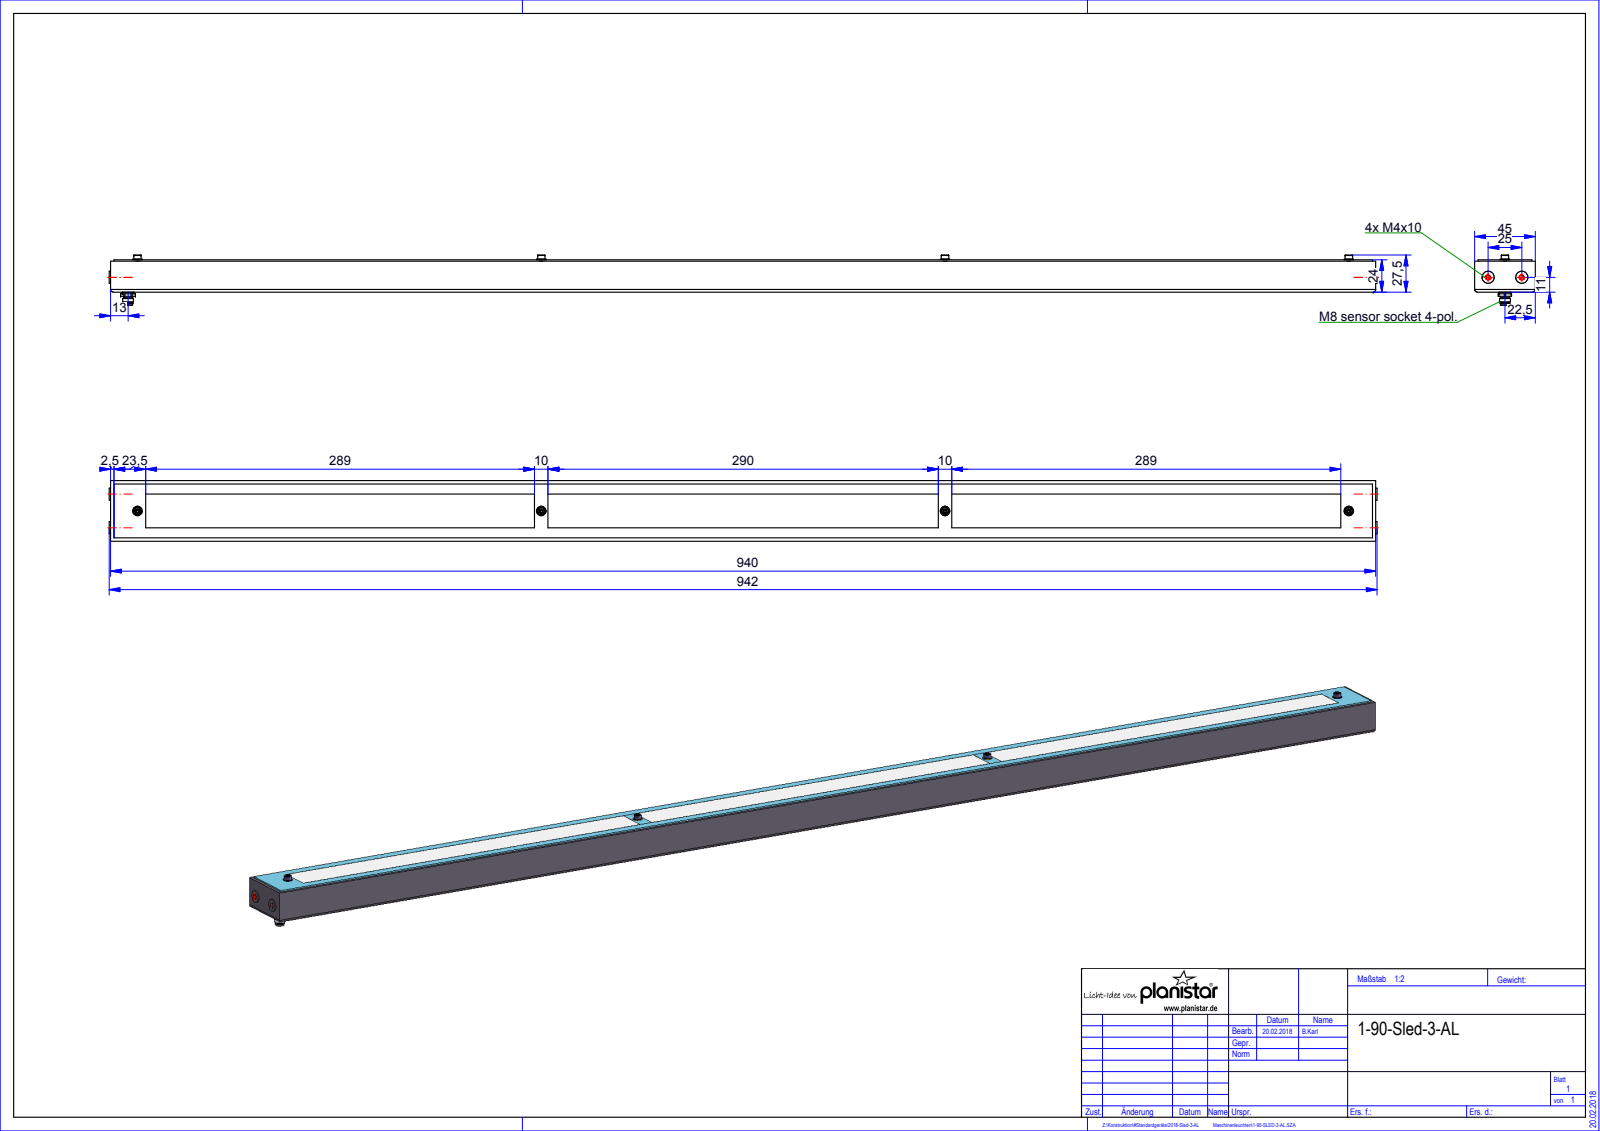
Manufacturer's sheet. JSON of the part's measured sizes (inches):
{"part_name": "Root; Baugruppe_Xled-2-VD; QUADER_0; 09-3391-00-04 (+2 more)", "step_written_by": "HiCAD 2015 2002.1 Build 408 (AUTOMOTIVE_DESIGN)", "units": "inches", "bodies": {"solids": 10, "faces": 192, "planar": 70, "cylindrical": 101, "other": 21}, "overall_size": [37.087, 1.772, 1.465], "volume_in3": 61.51, "surface_area_in2": 205.8, "round_holes": [[0.126, 4], [0.13, 2], [0.157, 2], [0.228, 1]], "round_bosses_or_shafts": [[0.276, 4], [0.217, 4], [0.118, 4], [0.097, 4], [0.039, 4], [0.354, 2], [0.315, 1], [0.283, 1]], "partial_cylinders_radius": [[0.009, 24], [0.023, 24], [0.079, 4], [0.217, 1]], "face_to_face_distances": [0.943, 1.772, 0.945, 0.039, 0.906, 0.037, 0.098, 1.673, 1.575, 37.008], "hole_center_spacings": [11.811, 23.622, 0.276, 0.984, 12.087, 23.898, 35.433, 35.709]}
